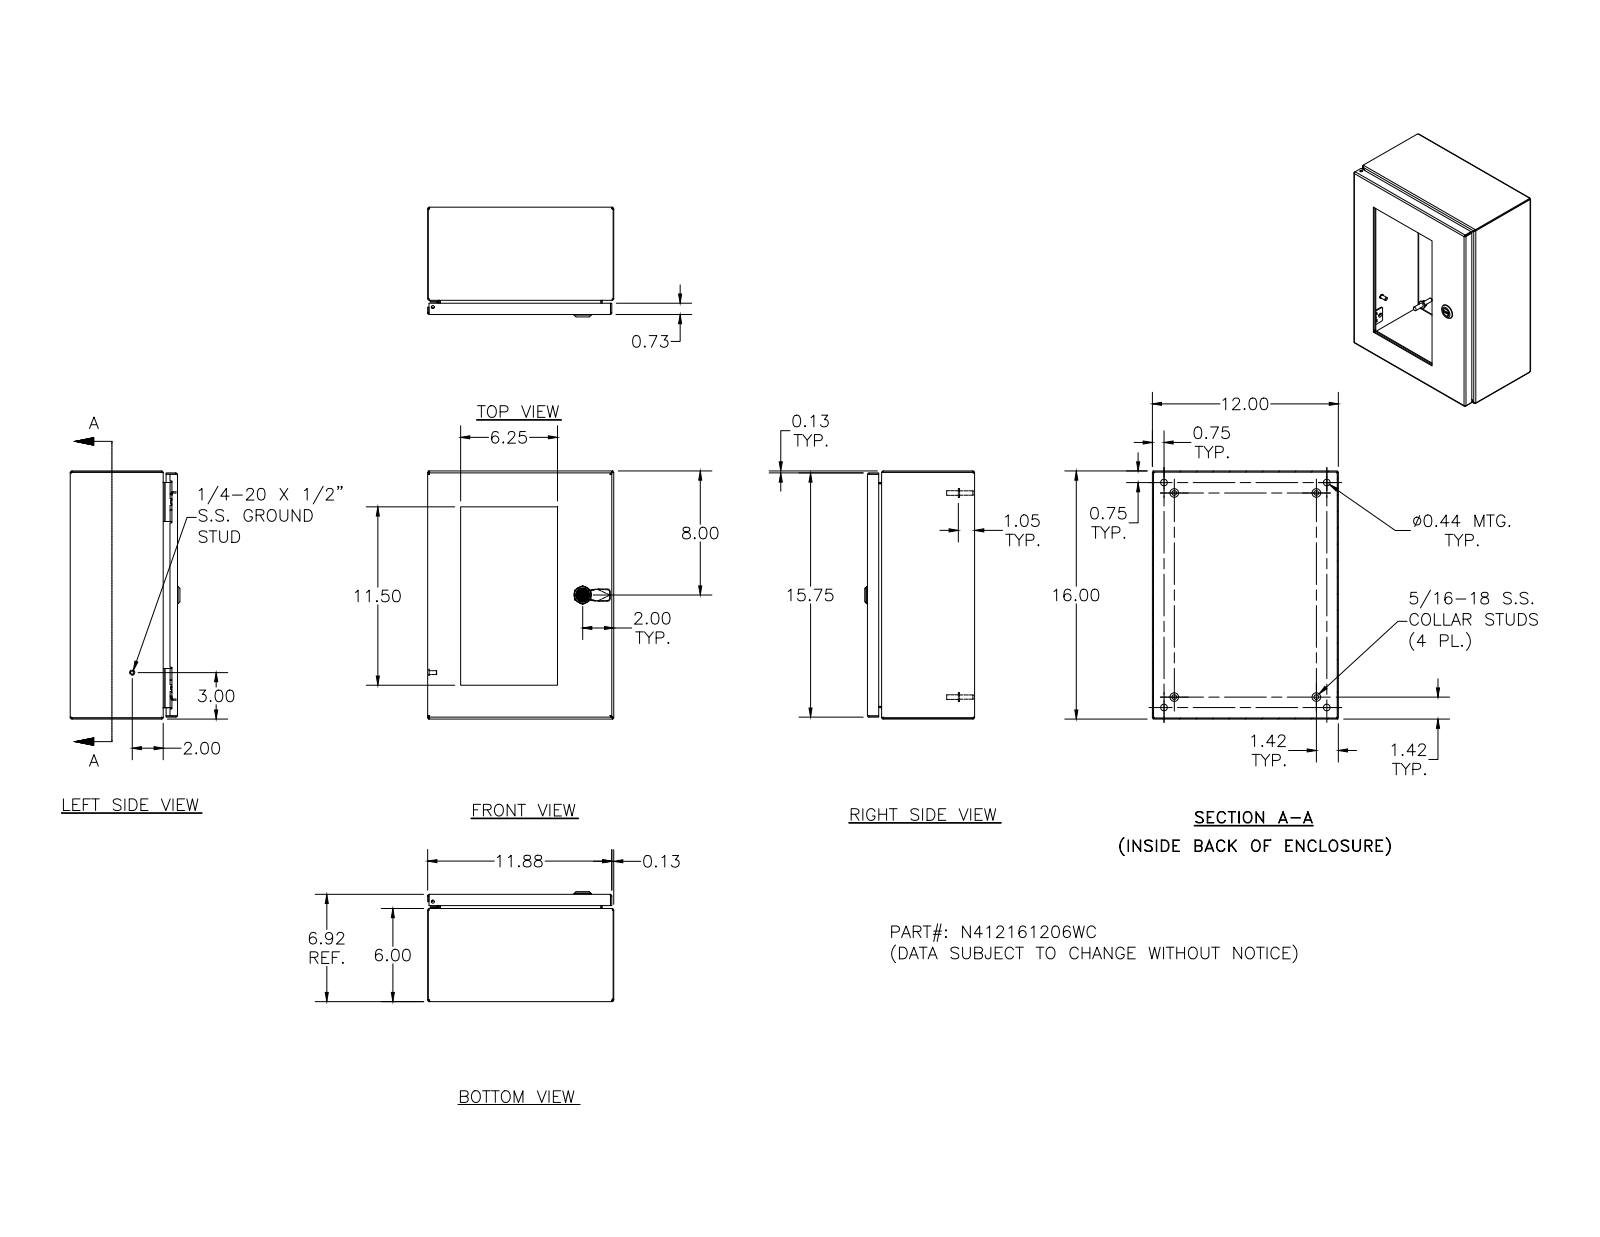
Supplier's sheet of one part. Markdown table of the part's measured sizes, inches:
| quantity | value |
| --- | --- |
| part name | N412161206WC |
| STEP written by | SolidWorks 2018 (AUTOMOTIVE_DESIGN) |
| units | inches |
| bodies | 57 solids, 1827 faces (687 planar, 593 cylindrical, 547 other) |
| overall size | 16 × 12 × 7.075 |
| volume | 82.94 in³ |
| surface area | 1 846 in² |
| round holes (diameter × count) | 0.156 × 12, 0.281 × 10, 0.188 × 5, 0.093 × 4, 0.152 × 4, 0.167 × 4, 0.172 × 4, 0.437 × 4, 0.187 × 1, 0.197 × 1, 0.315 × 1, 0.394 × 1 |
| round bosses / shafts (diameter × count) | 0.337 × 10, 0.25 × 10, 0.19 × 10, 0.563 × 4, 0.36 × 4, 0.32 × 4, 0.3 × 4, 0.275 × 4 |
| partial cylindrical surfaces (radius × count) | 0.031 × 34, 0.012 × 30, 0.05 × 26, 0.105 × 24, 0.016 × 18, 0.125 × 16, 0.02 × 13, 0.032 × 8 |
| main face-to-face distances | 0.074, 6.843, 6.769, 11.926, 15.926, 6.917, 12, 11.852, 0.25, 6.593 |
| hole center spacings | 4, 12, 6.221, 8.5, 8.585, 11.862, 7.5, 0.5 |
